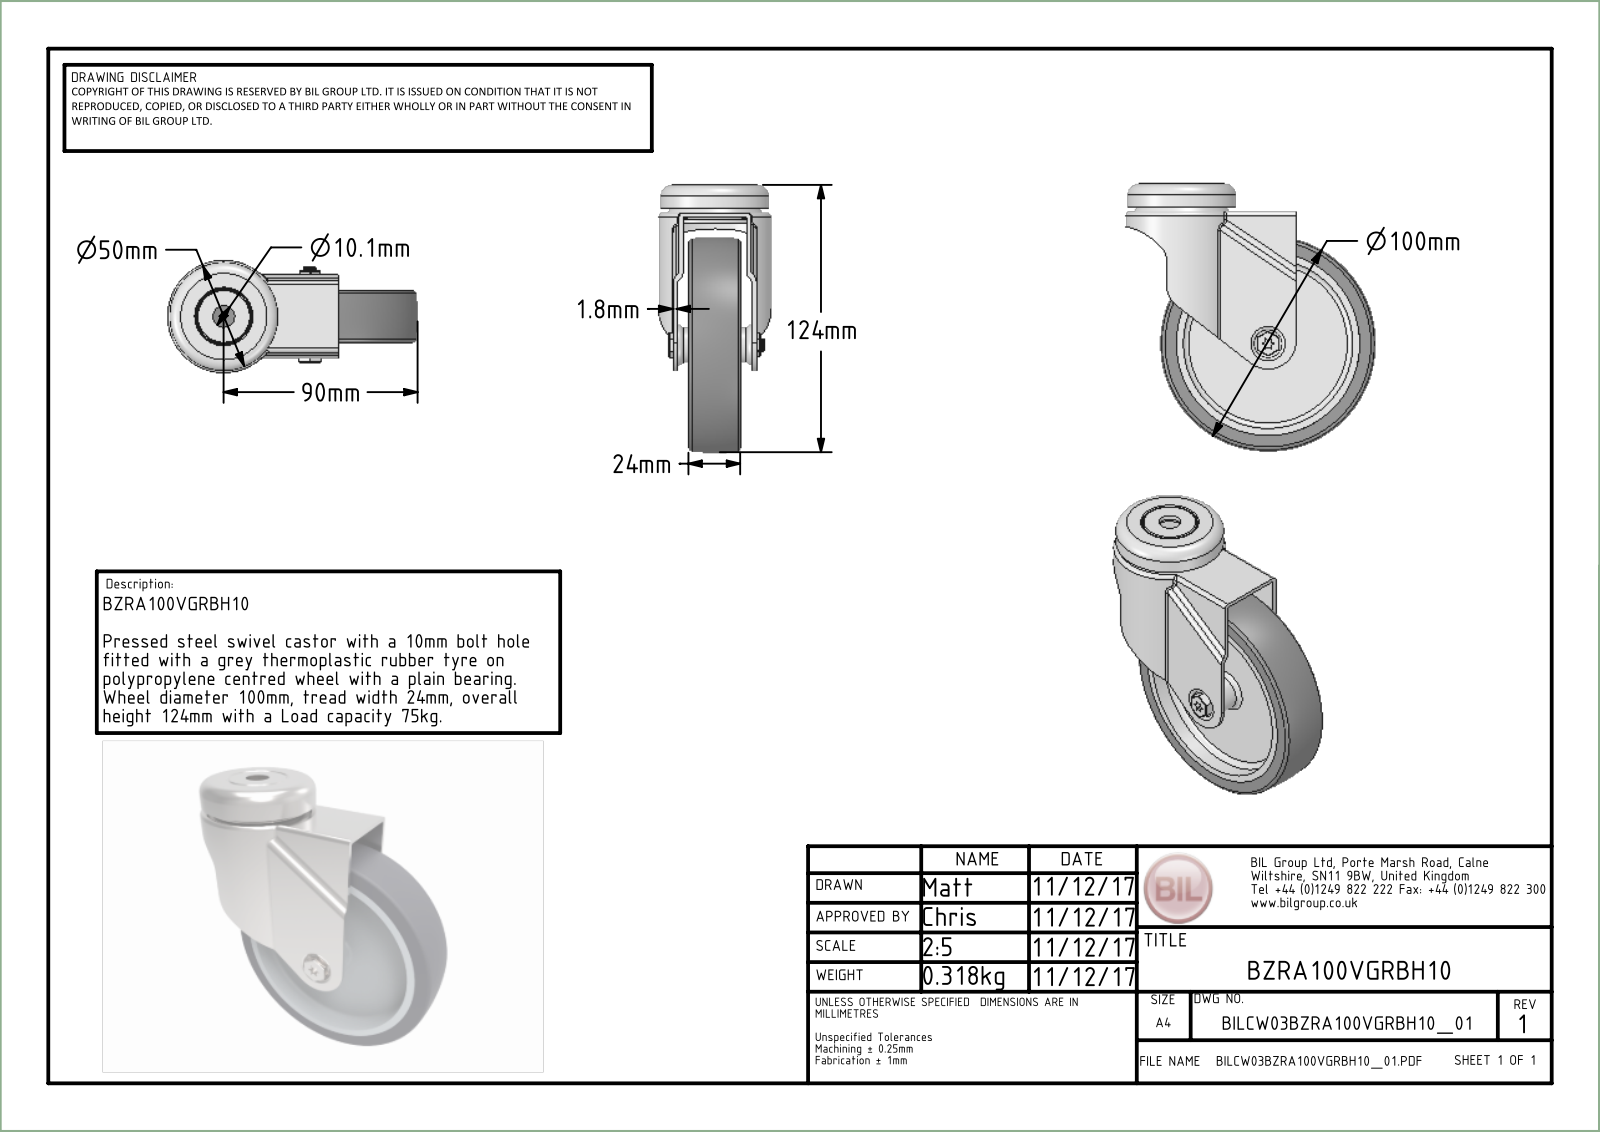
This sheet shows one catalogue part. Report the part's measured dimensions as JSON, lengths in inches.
{"part_name": "BZRA100VGRBH10 v3; BZRA100ASBH10 v1; ZINC PLATED PRESSED STEEL HEAD; ZINC PLATED PRESSED STEEL FORKS (+8 more)", "step_written_by": "Autodesk Translation Framework v13.20.0.188 (AP242_MANAGED_MODEL_BASED_3D_ENGINEERING_MIM_LF)", "units": "inches", "bodies": {"solids": 7, "faces": 280, "planar": 61, "cylindrical": 107, "other": 112}, "overall_size": [4.882, 4.528, 1.969], "volume_in3": 8.394, "surface_area_in2": 112.2, "round_holes": [[0.236, 1], [0.248, 1], [0.252, 1], [0.323, 1], [0.327, 1], [0.413, 1], [0.416, 1], [1.181, 1], [3.258, 1]], "round_bosses_or_shafts": [[3.937, 1], [1.535, 1], [0.709, 1], [0.591, 1], [0.581, 1], [0.315, 1], [0.313, 1], [0.231, 1]], "partial_cylinders_radius": [[0.039, 18], [0.071, 18], [0.02, 12], [0.016, 6], [0.035, 2], [0.083, 1], [0.197, 1], [0.276, 1]], "face_to_face_distances": [0.236, 0.071, 0.354, 0.591, 1.331, 0.287, 0.642, 0.878, 1.232, 0.118]}
